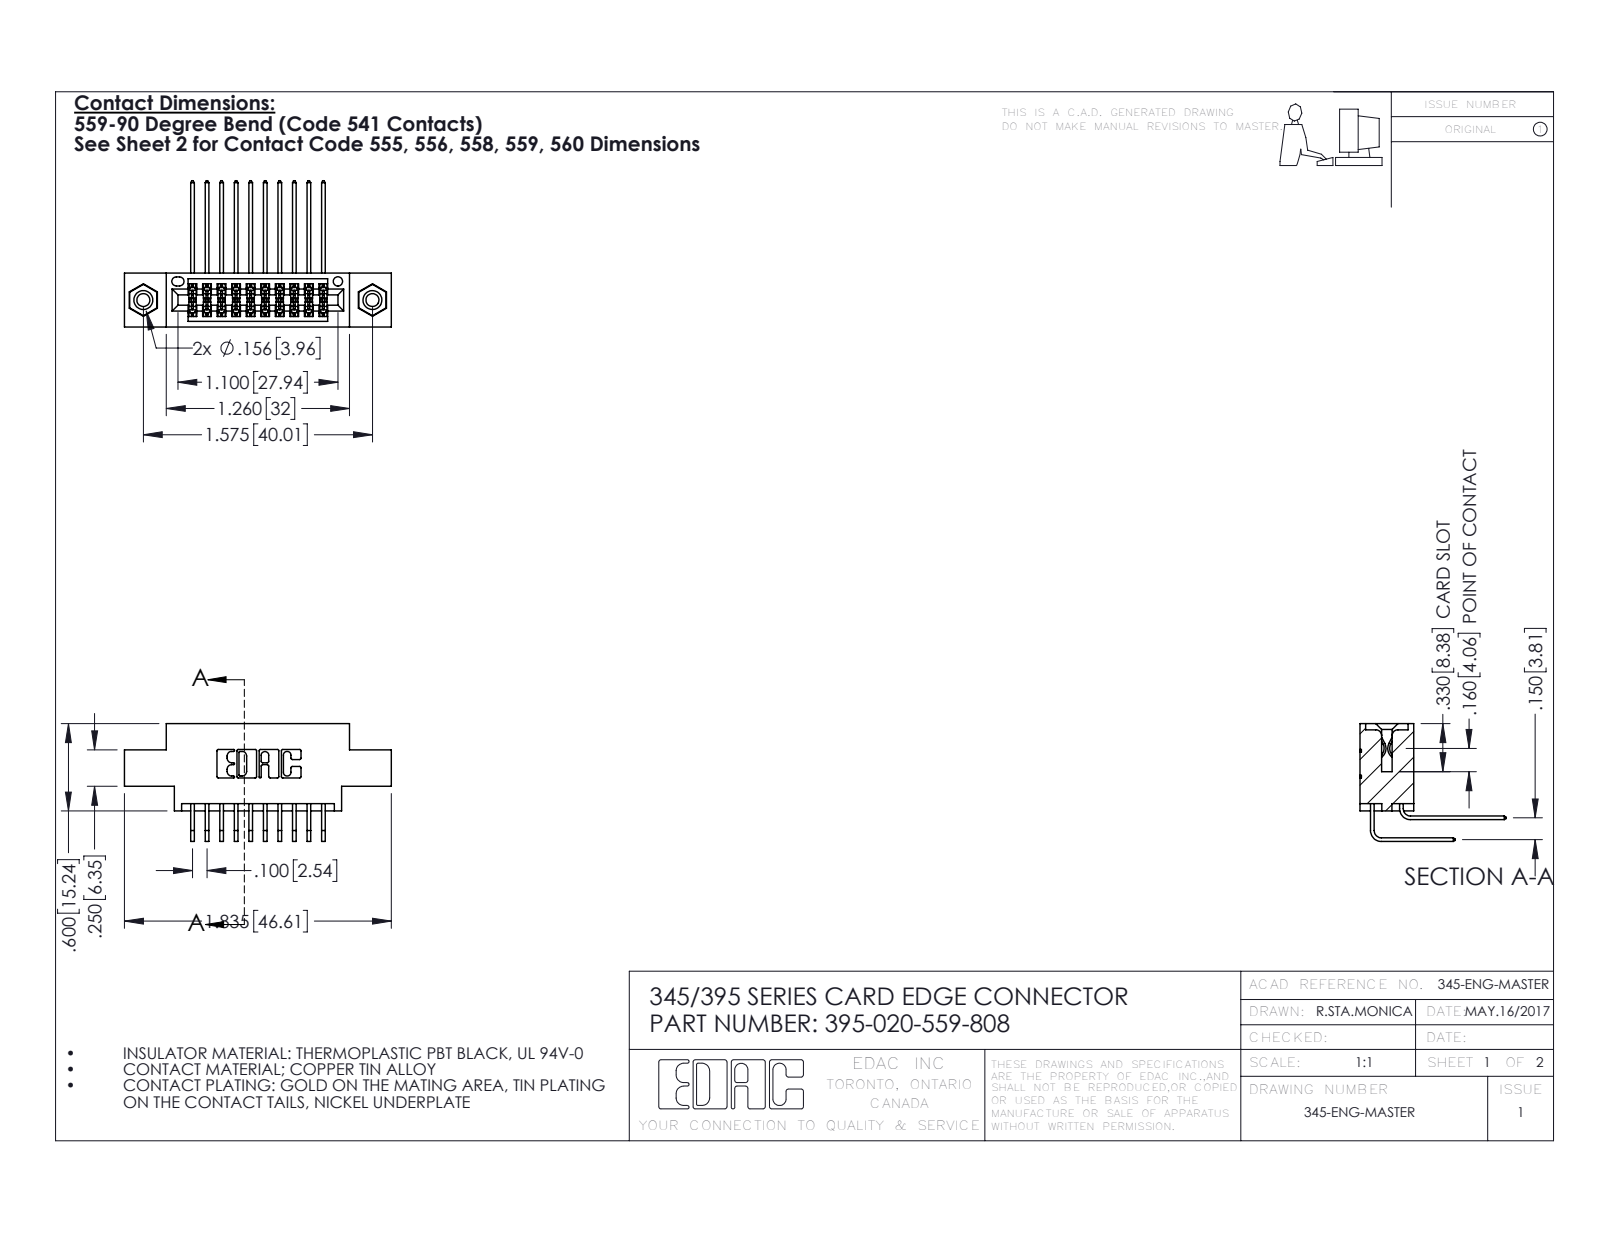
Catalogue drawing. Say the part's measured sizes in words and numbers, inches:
The part is named "345-250-001_345-250-003-102; 345-292-001_559 Tail - 2; 395-020-559-808; 345 Part_0.170 Offset - 0.156 Dia-TI (+1 more)". Its 3-D file was written by "SolidWorks 2016 (CONFIG_CONTROL_DESIGN)". It is 23 solids with 1230 faces: 816 planar, 398 cylindrical and 16 other. Overall it measures 1.835 by 1.005 by 0.809 inches. Its volume is 0.258 cubic inches and its surface area 9.806 square inches. Round holes: 2 of diameter 0.089, 2 of diameter 0.125, 2 of diameter 0.156, 1 of diameter 0.064. Round bosses or shafts: 2 of diameter 0.155. Partial cylindrical surfaces (rounded edges, fillets, slot ends): 31 of radius 0.006, 22 of radius 0.01, 6 of radius 0.007, 6 of radius 0.031, 3 of radius 0.026, 2 of radius 0.014, 2 of radius 0.019, 2 of radius 0.022. The main face-to-face distances are 0.072, 0.298, 0.37, 0.2, 0.098, 0.272, 0.025, 0.15, 0.1, 0.175. The hole center spacings are 0.27, 1.344, 1.575.
